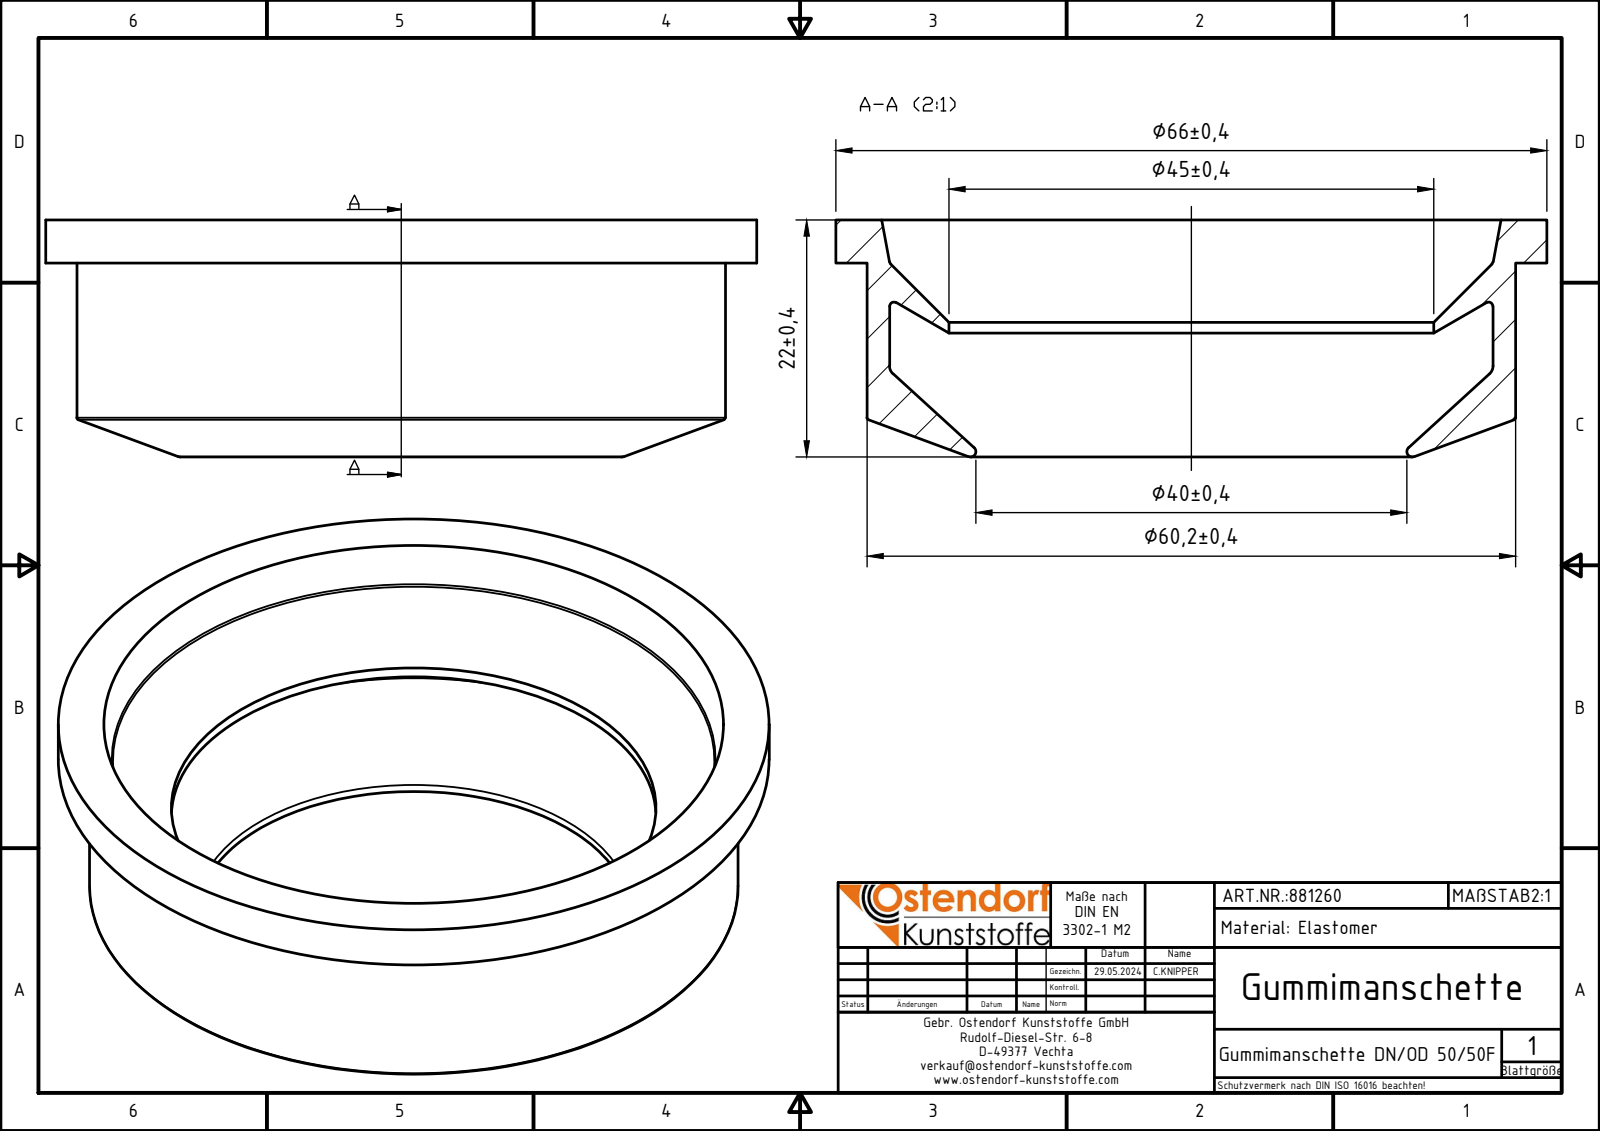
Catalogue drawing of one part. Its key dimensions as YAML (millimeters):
part_name: "881260z"
step_written_by: "Autodesk Inventor 2024 (AUTOMOTIVE_DESIGN)"
units: millimeters
bodies: {solids: 1, faces: 16, planar: 2, cylindrical: 4, other: 10}
overall_size: [66, 66, 22]
volume: 15093
surface_area: 12521
round_holes:
  - {diameter: 45, count: 1}
  - {diameter: 56, count: 1}
round_bosses_or_shafts:
  - {diameter: 66, count: 1}
  - {diameter: 60.2, count: 1}
face_to_face_distances: [4]
